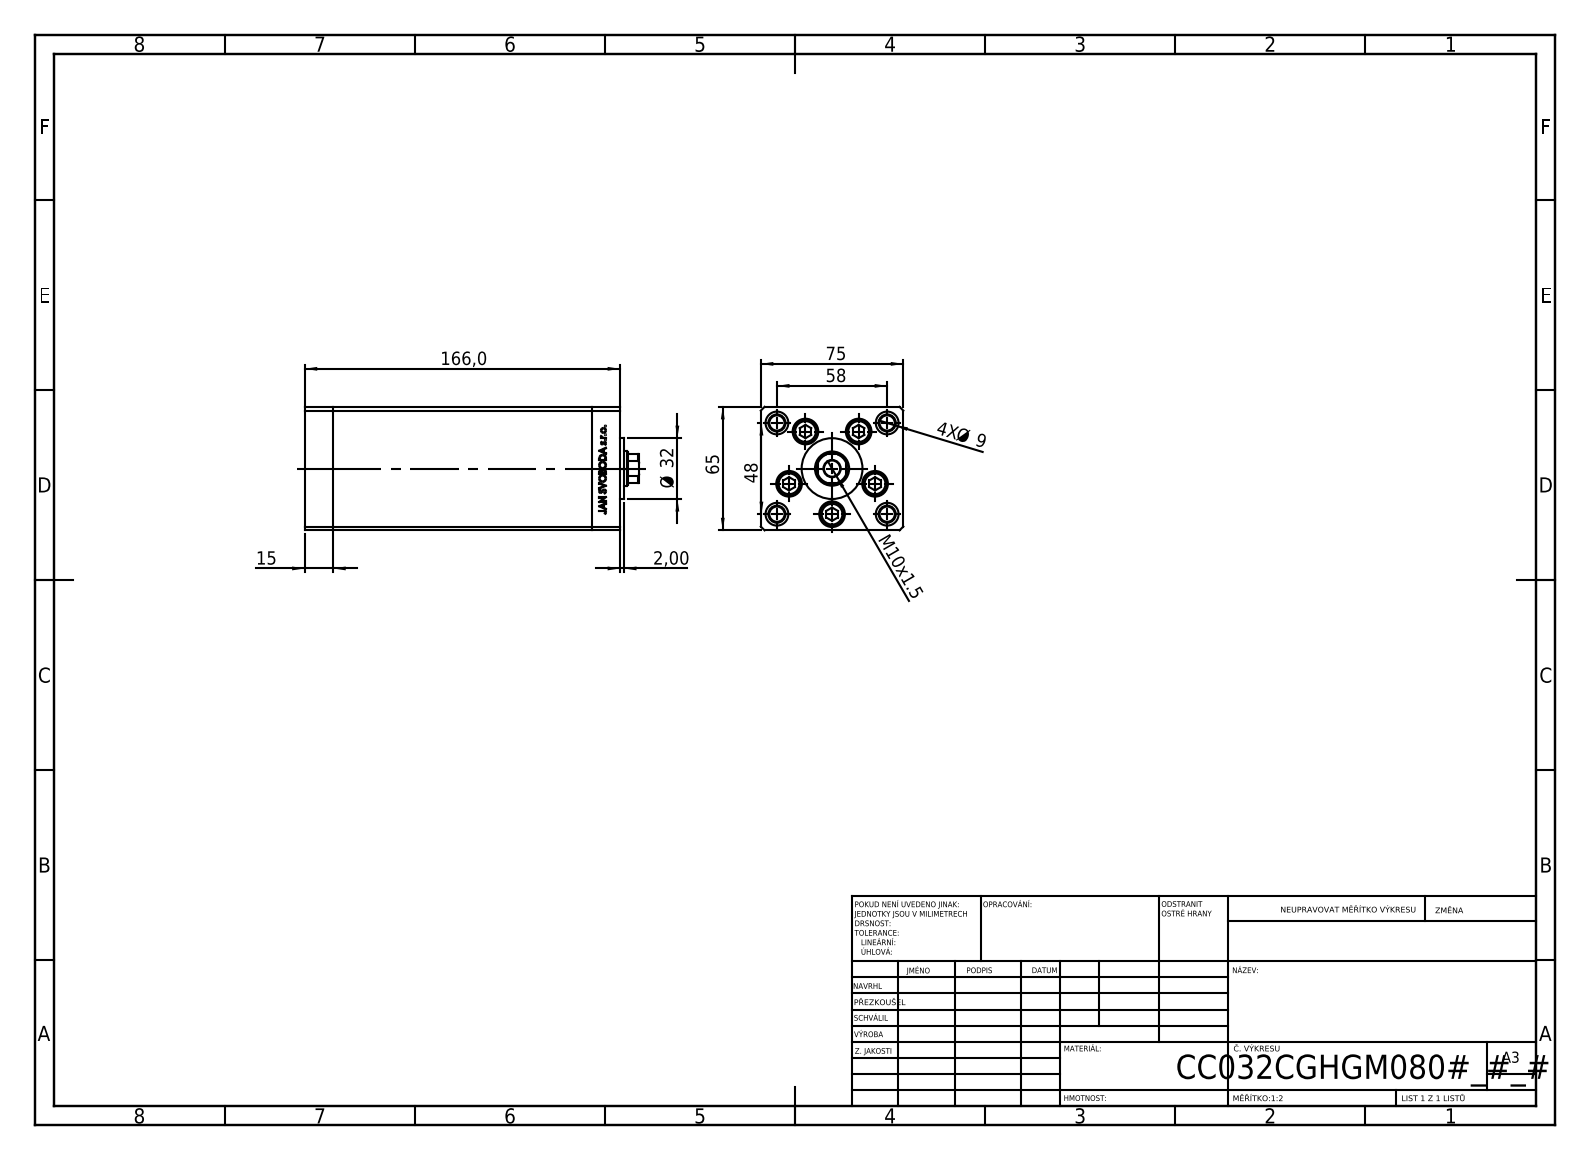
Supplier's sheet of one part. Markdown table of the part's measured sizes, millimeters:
| quantity | value |
| --- | --- |
| part name | V220C FRONT; ALLEN BOLT; V220C_VC_C; V220C BACK_C (+1 more) |
| STEP written by | SolidWorks 2019 (CONFIG_CONTROL_DESIGN) |
| units | millimeters |
| bodies | 13 solids, 1179 faces (542 planar, 175 cylindrical, 462 other) |
| overall size | 176 × 75 × 65 |
| volume | 676 888 mm³ |
| surface area | 143 721 mm² |
| round holes (diameter × count) | 9 × 9, 13.5 × 5, 2 × 4, 8 × 4, 12 × 4, 13.16 × 4, 8.5 × 1, 12.5 × 1, 18 × 1 |
| round bosses / shafts (diameter × count) | 8 × 5, 12.5 × 4, 32 × 1 |
| partial cylindrical surfaces (radius × count) | 0.93 × 2, 8.5 × 1 |
| main face-to-face distances | 75, 65, 15, 136, 151, 166, 28, 13, 142, 9 |
| hole center spacings | 24, 37.64, 15.67, 17.22, 27.71, 28.83, 29, 32.63 |
